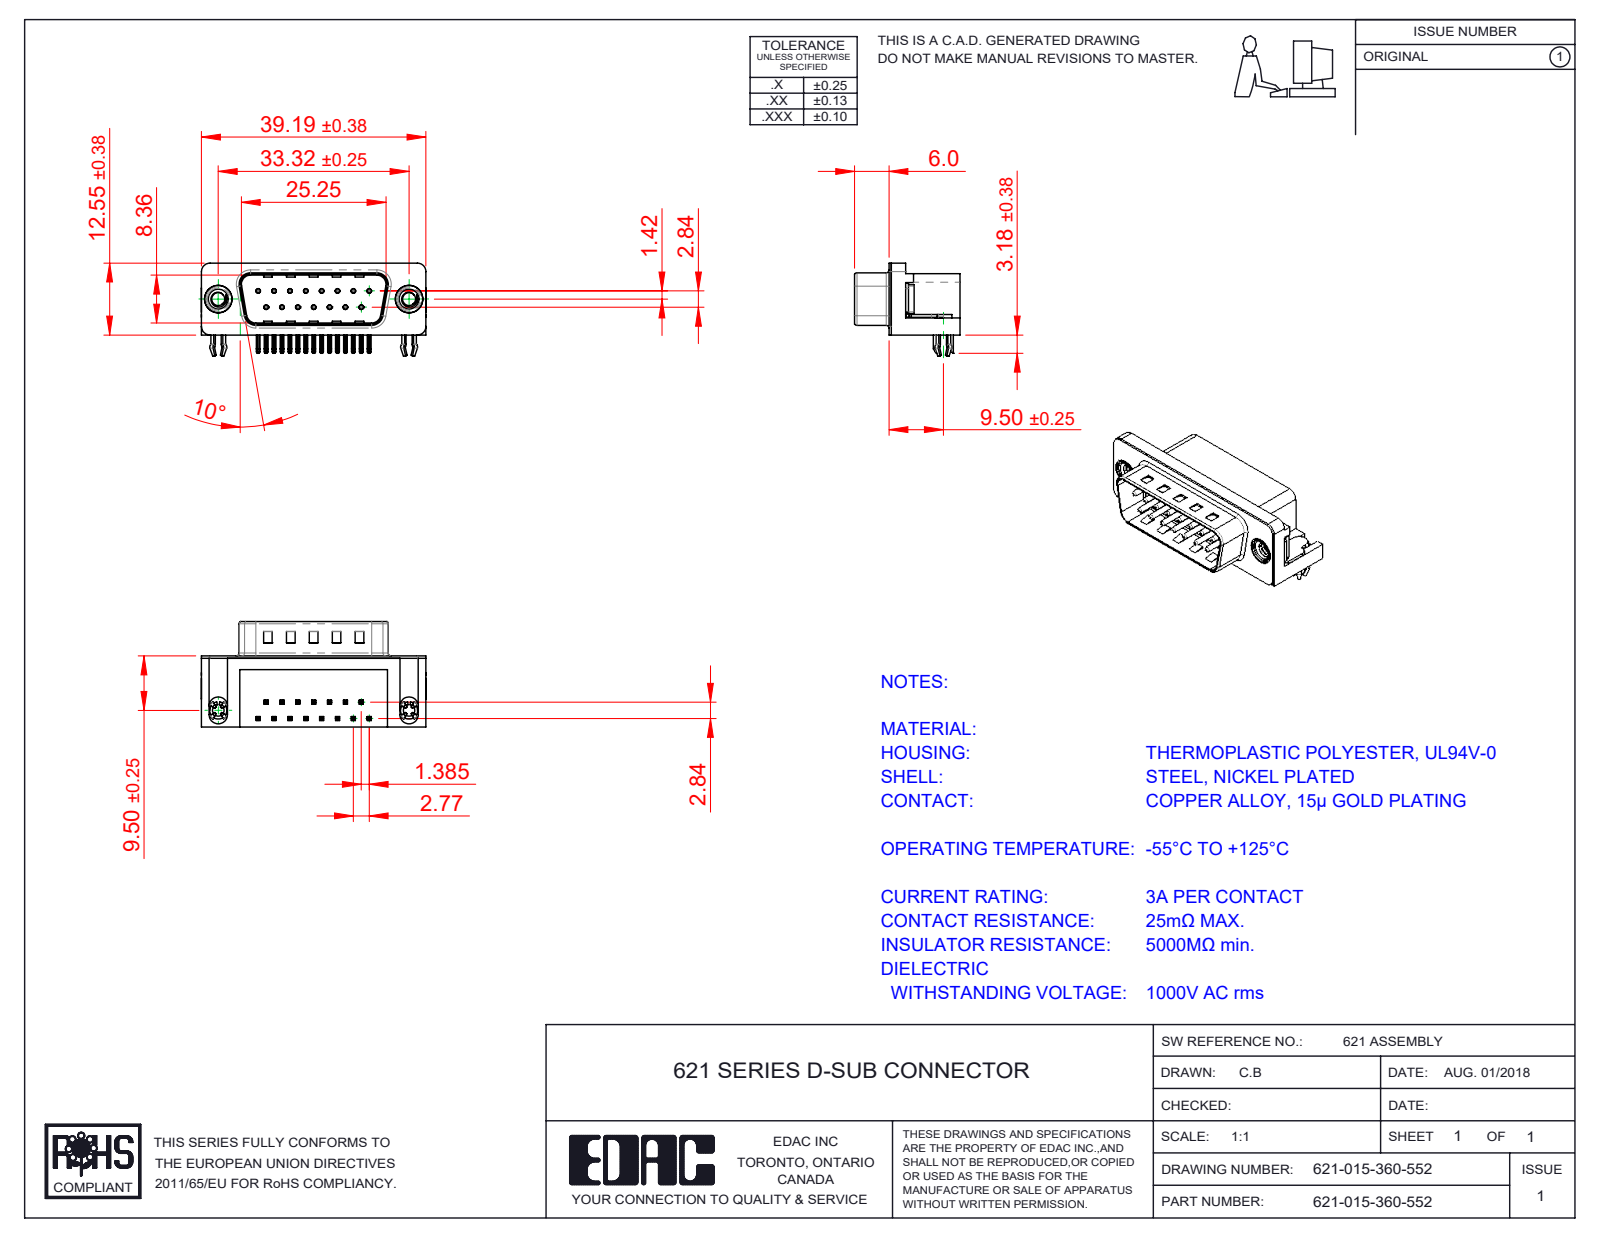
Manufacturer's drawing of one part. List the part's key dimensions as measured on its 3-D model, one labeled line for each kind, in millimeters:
Part name (STEP PRODUCT): 621 Contact Bottom; 621 4-40 Threaded Rivet; 621 Housing_15 Socket; 621 Shell_15 Socket (+3 more)
STEP written by: SolidWorks 2016 (CONFIG_CONTROL_DESIGN)
Units: millimetres
Bodies: 21 solids, 1507 faces (893 planar, 457 cylindrical, 157 other)
Overall size (bounding box): 39.22 × 18.4 × 15.73
Volume: 4 428 mm³ · Surface area: 5 730 mm²
Round holes (diameter × count): ⌀0.35 ×15, ⌀0.8 ×15, ⌀2.26 ×4, ⌀4 ×2, ⌀4.8 ×2, ⌀5 ×2
Round bosses / shafts (diameter × count): ⌀0.75 ×15, ⌀4.9 ×2, ⌀4.75 ×2, ⌀3.9 ×2, ⌀3.26 ×2
Partial cylindrical surfaces — rounded edges, fillets, slot ends (radius × count): R0.25 ×68, R0.12 ×30, R1 ×16, R0.5 ×9, R1.6 ×8, R1.5 ×6, R0.9 ×4, R2 ×4
Main face-to-face distances: 0.4, 12, 10.35, 2.1, 10.46, 12.4, 1.7, 10.86, 8.76, 2.9
Hole centre spacings: 3.16, 2.77, 5.54, 8.31, 11.08, 5.03, 5.04, 7.48
